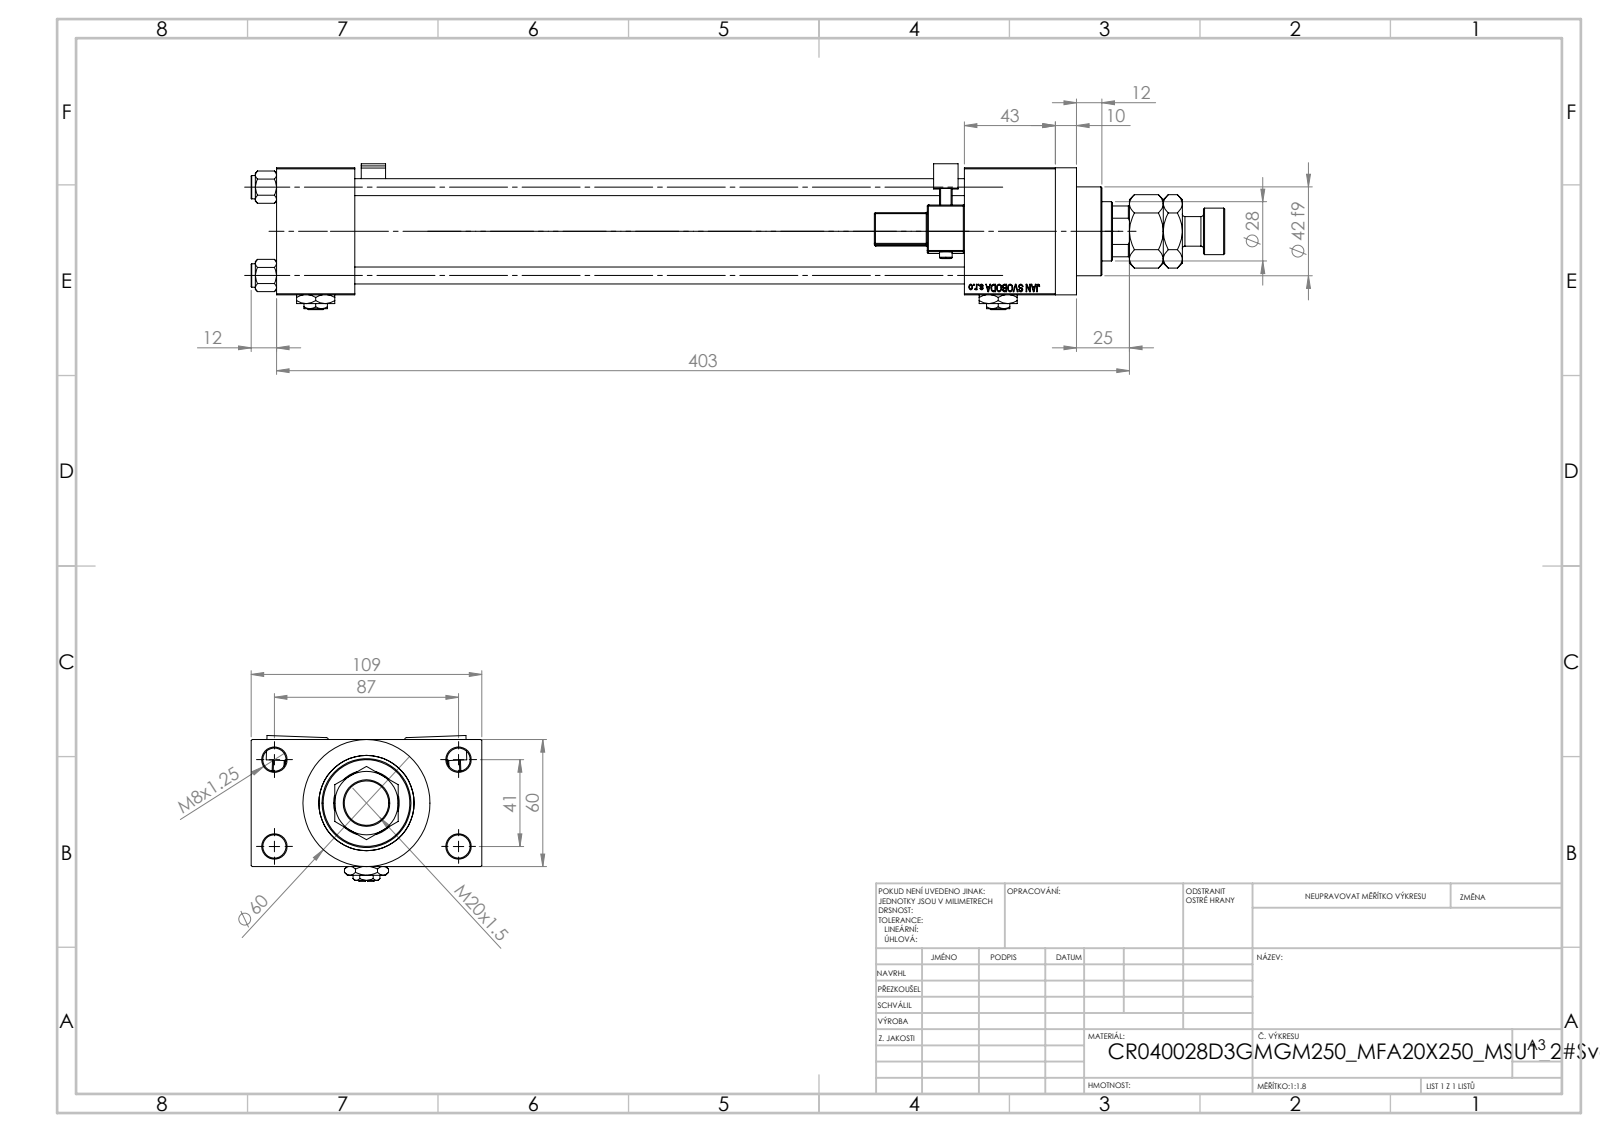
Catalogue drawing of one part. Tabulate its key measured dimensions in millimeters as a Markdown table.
| quantity | value |
| --- | --- |
| part name | V215CR_D_Body; NUT_M5_D; V215CR_MSU; Zatka_pro_OIL_PORT (+4 more) |
| STEP written by | SolidWorks 2019 (CONFIG_CONTROL_DESIGN) |
| units | millimeters |
| bodies | 16 solids, 1411 faces (620 planar, 163 cylindrical, 628 other) |
| overall size | 460 × 109 × 68.9 |
| volume | 873 563 mm³ |
| surface area | 254 835 mm² |
| round holes (diameter × count) | 8 × 4, 11 × 4, 16.66 × 4, 24 × 4, 7 × 3, 18.5 × 1, 28 × 1, 31 × 1, 40 × 1, 45 × 1 |
| round bosses / shafts (diameter × count) | 11 × 4, 6 × 2, 60 × 1, 46 × 1, 42 × 1, 22 × 1, 14 × 1 |
| partial cylindrical surfaces (radius × count) | 0.5 × 48, 1 × 2, 2.5 × 2, 4 × 2, 13.5 × 1 |
| main face-to-face distances | 60, 288, 24.5, 84.5, 37, 325, 368, 331, 43, 15 |
| hole center spacings | 22.65, 29.49, 41.7, 47.15, 48.09, 64.35, 76.49, 41 |
